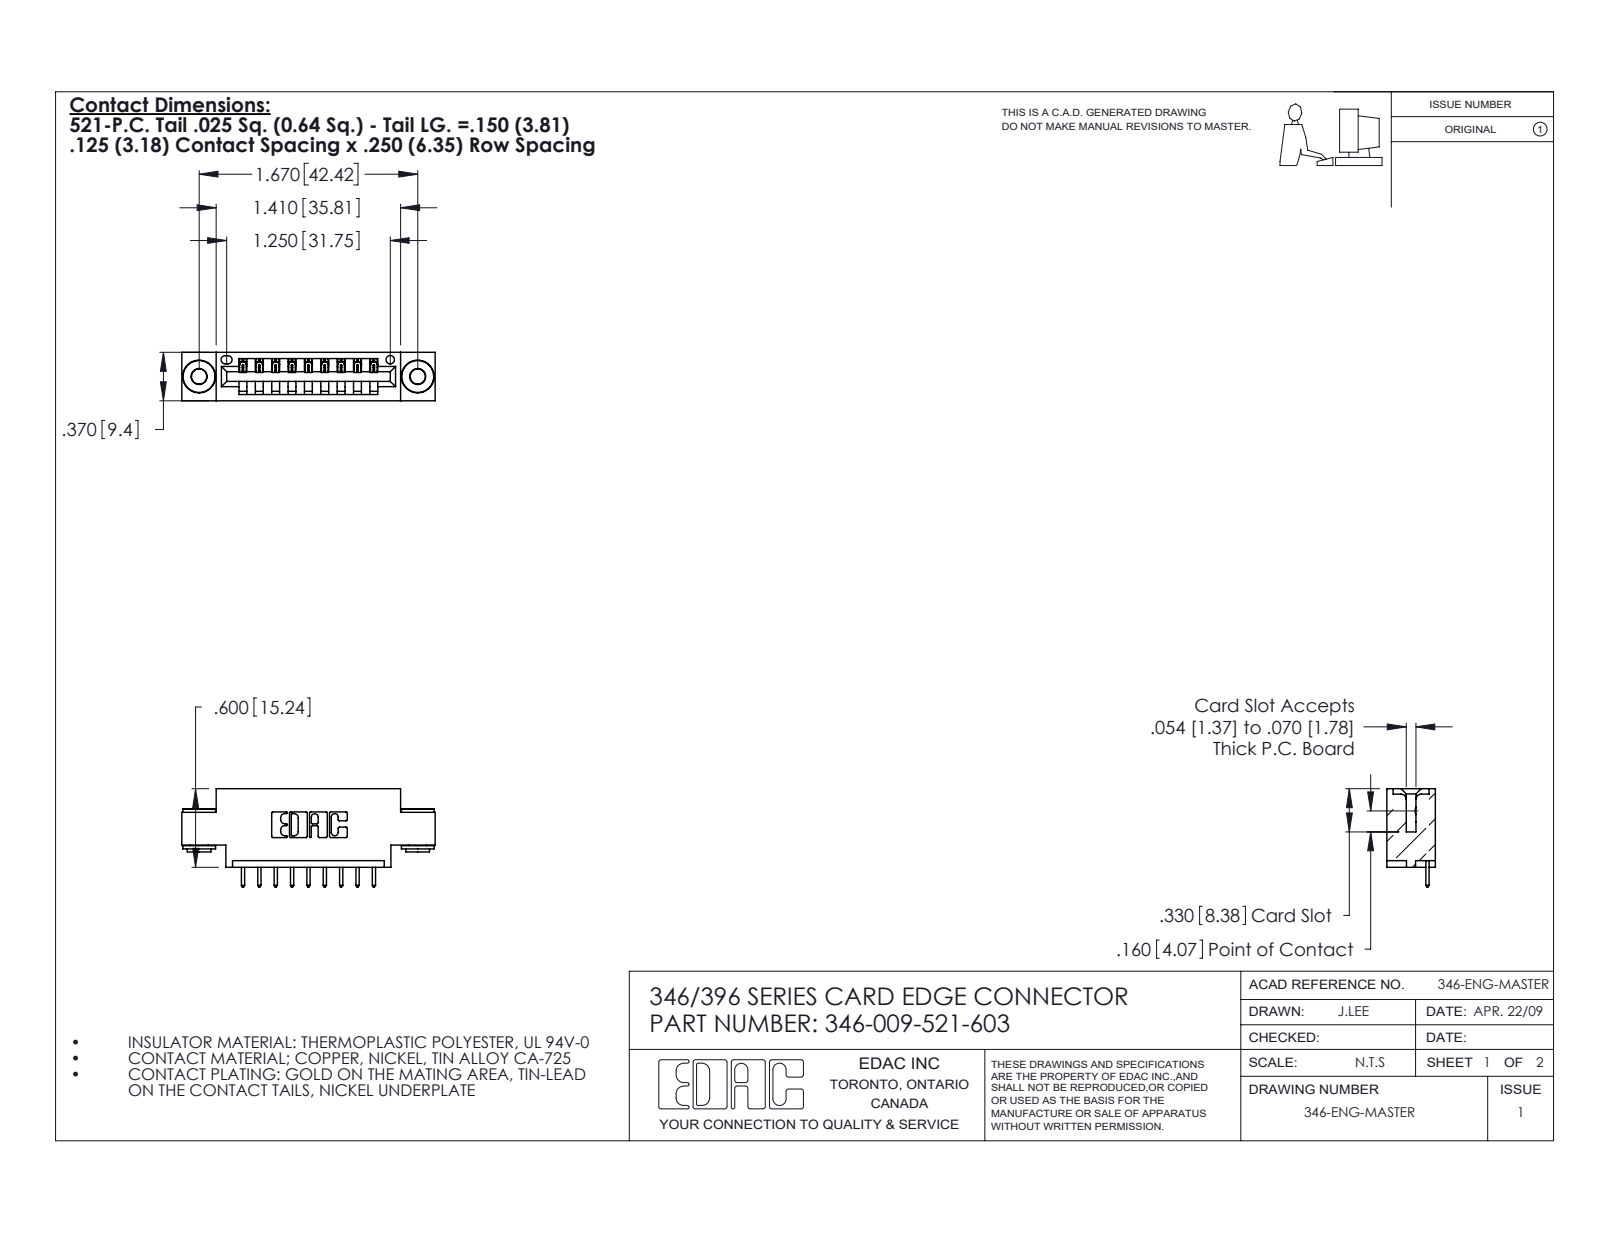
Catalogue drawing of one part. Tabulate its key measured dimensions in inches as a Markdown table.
| quantity | value |
| --- | --- |
| part name | 345-250-002_345-250-002-102; 346 Part_0.170 Offset - 0.156 Dia-TH; 346-009-521-603; 345-292-001_345-293-121 |
| STEP written by | SolidWorks 2020 (CONFIG_CONTROL_DESIGN) |
| units | inches |
| bodies | 12 solids, 700 faces (464 planar, 228 cylindrical, 8 other) |
| overall size | 1.935 × 0.75 × 0.37 |
| volume | 0.262 in³ |
| surface area | 8.256 in² |
| round holes (diameter × count) | 0.116 × 2, 0.156 × 2, 0.064 × 1 |
| round bosses / shafts (diameter × count) | 0.25 × 2, 0.18 × 2, 0.136 × 2 |
| partial cylindrical surfaces (radius × count) | 0.01 × 22, 0.006 × 18, 0.01 × 18, 0.007 × 6, 0.031 × 6, 0.026 × 3, 0.031 × 2, 0.04 × 2 |
| main face-to-face distances | 0.25, 0.37, 0.048, 0.322, 0.025, 0.222, 0.148, 0.1, 0.174, 0.072 |
| hole center spacings | 0.246, 1.465, 1.67 |
